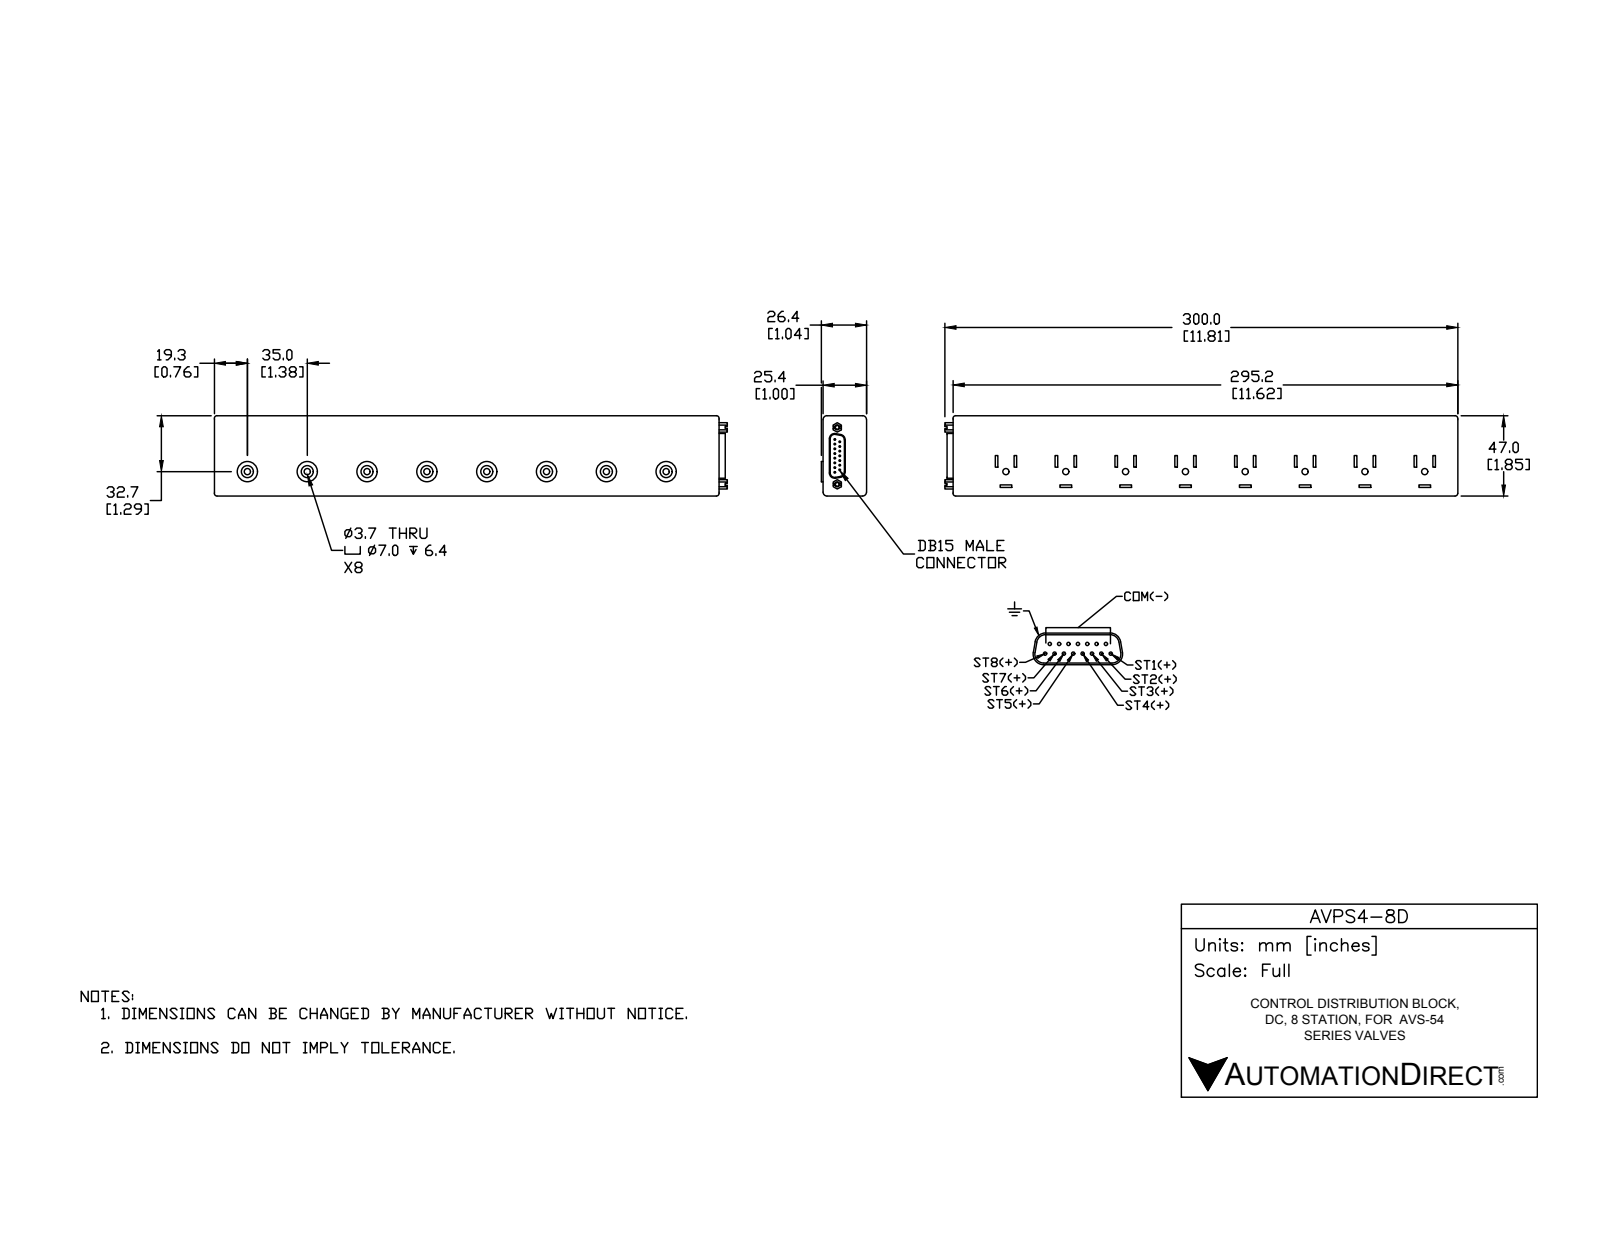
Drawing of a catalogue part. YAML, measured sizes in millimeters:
part_name: "AVPS4-8D"
step_written_by: "SolidWorks 2016 (AUTOMOTIVE_DESIGN)"
units: millimeters
bodies: {solids: 1, faces: 311, planar: 195, cylindrical: 104, other: 12}
overall_size: [300.1, 47, 26.4]
volume: 346300
surface_area: 50550
round_holes:
  - {diameter: 3.7, count: 8}
  - {diameter: 7, count: 8}
  - {diameter: 2.3, count: 2}
round_bosses_or_shafts:
  - {diameter: 1, count: 15}
  - {diameter: 11.9, count: 8}
partial_cylinders:
  - {radius: 1.6, count: 6}
  - {radius: 2.3, count: 4}
  - {radius: 2.6, count: 4}
  - {radius: 3.1, count: 4}
  - {radius: 1.6, count: 2}
face_to_face_distances: [25.4, 47, 295.2, 1, 26.4, 1.5, 35, 6.4, 20.1, 40.5]
hole_center_spacings: [35, 70, 105, 140, 175, 70, 105, 210]
